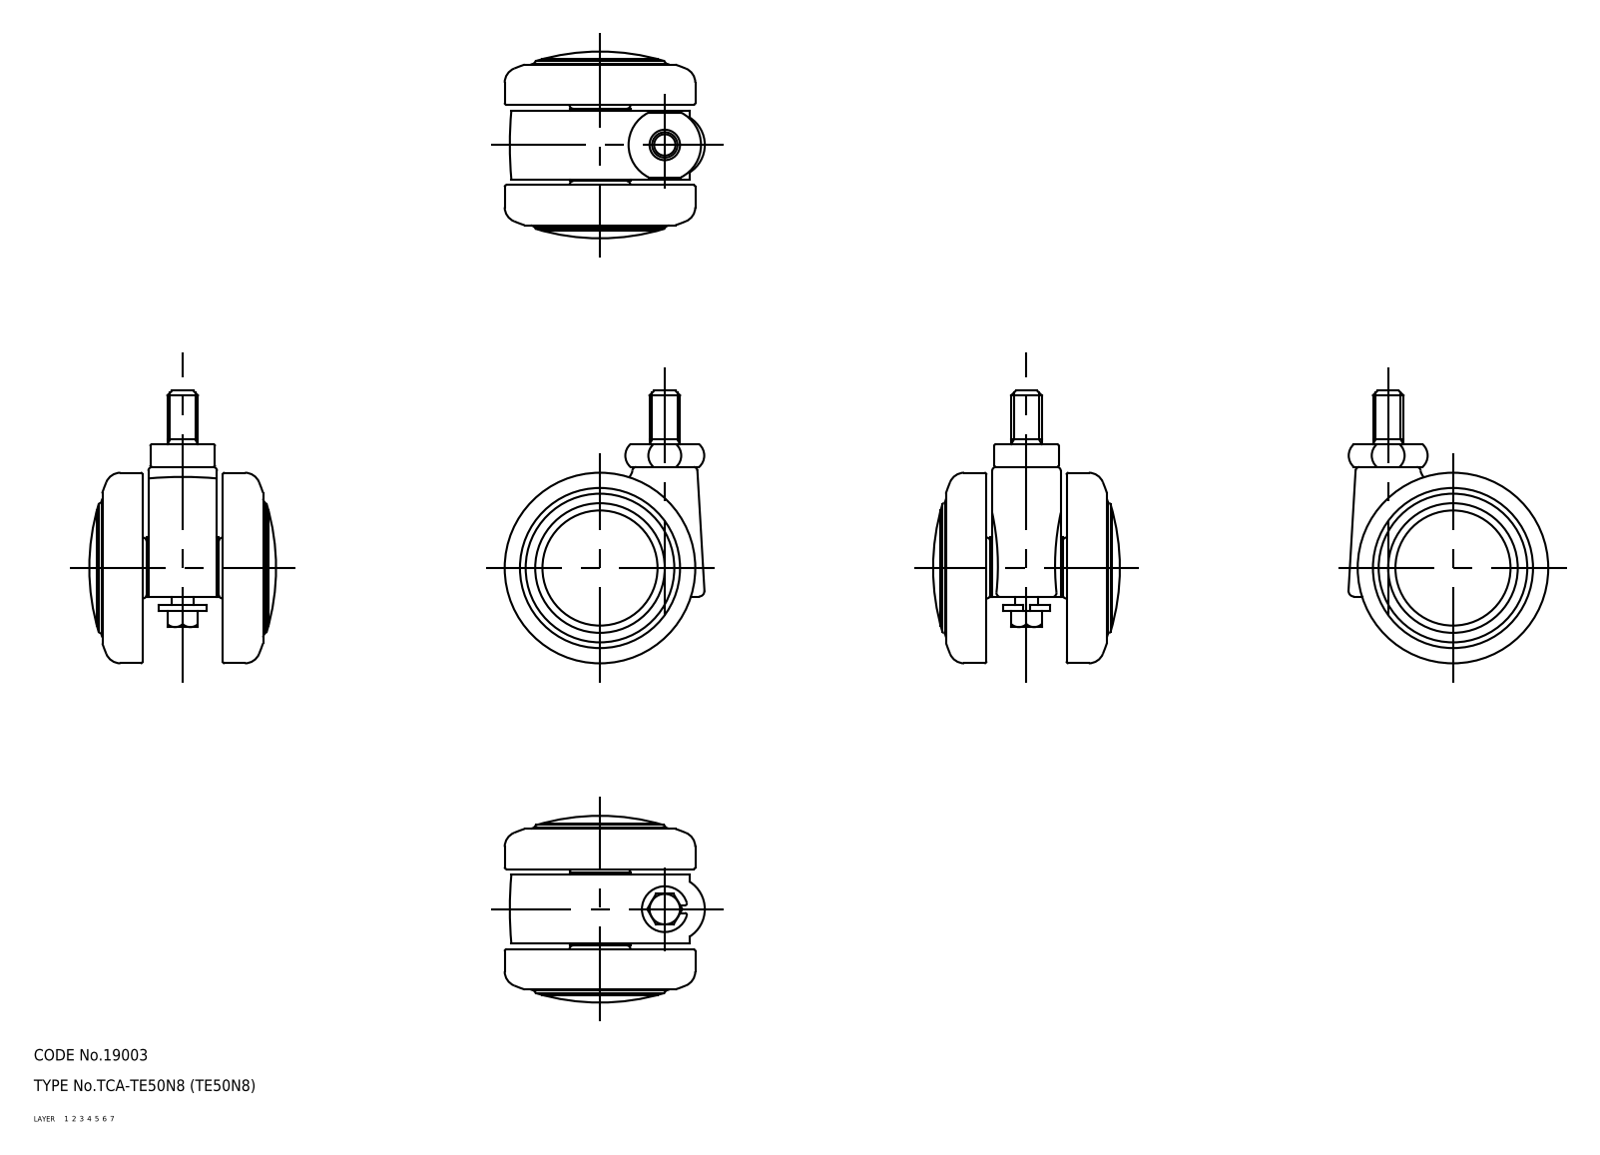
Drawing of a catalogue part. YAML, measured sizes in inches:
part_name: "wheel; main shaft; TE50N8_3523_36"
step_written_by: "CADfix (AUTOMOTIVE_DESIGN)"
units: inches
bodies: {solids: 4, faces: 136, planar: 0, cylindrical: 0, other: 136}
overall_size: [2.815, 2.064, 1.929]
volume: 3.819
surface_area: 39.72
